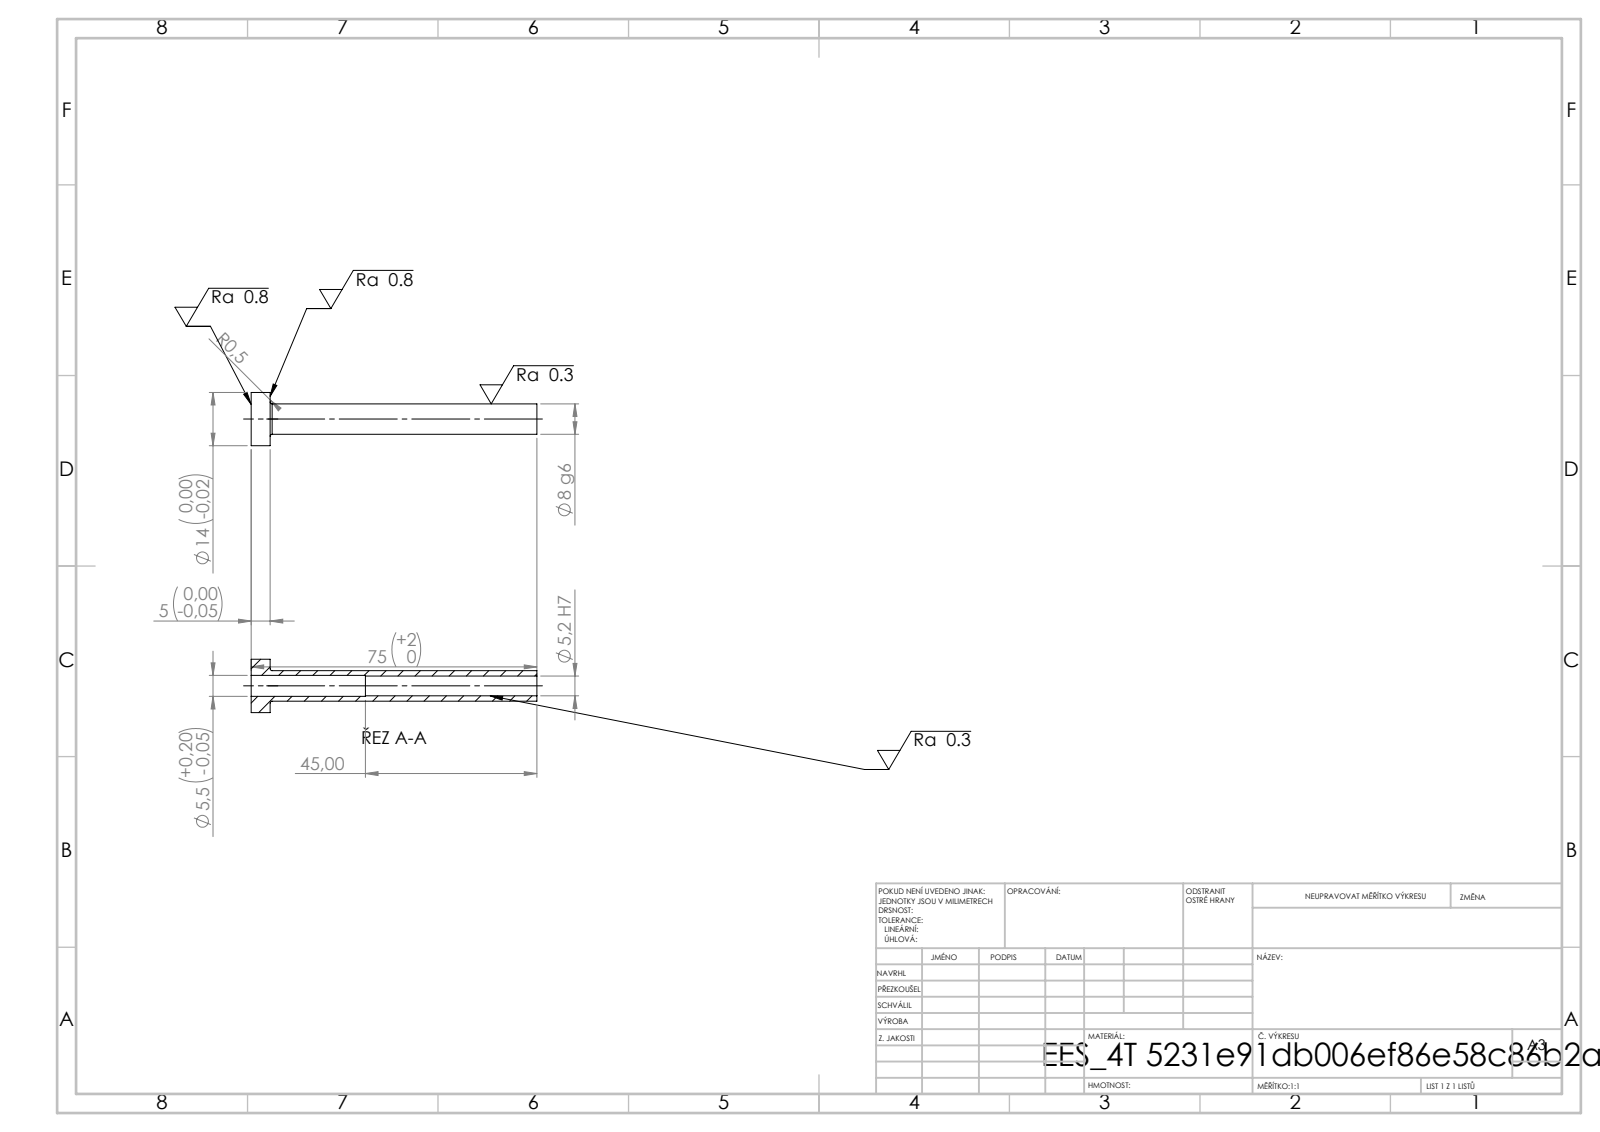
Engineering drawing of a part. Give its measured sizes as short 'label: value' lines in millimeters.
written by: SolidWorks 2019 (CONFIG_CONTROL_DESIGN)
unit: mm
bodies: 1 solid, 14 faces (4 planar, 8 cylindrical, 2 other)
size: 75 × 14 × 14
volume: 2 621 mm³; area: 3 493 mm²
holes: 1× ⌀5.2, 1× ⌀5.5
bosses: 1× ⌀14, 1× ⌀8
face distances: 5, 75, 70, 30, 25, 45
